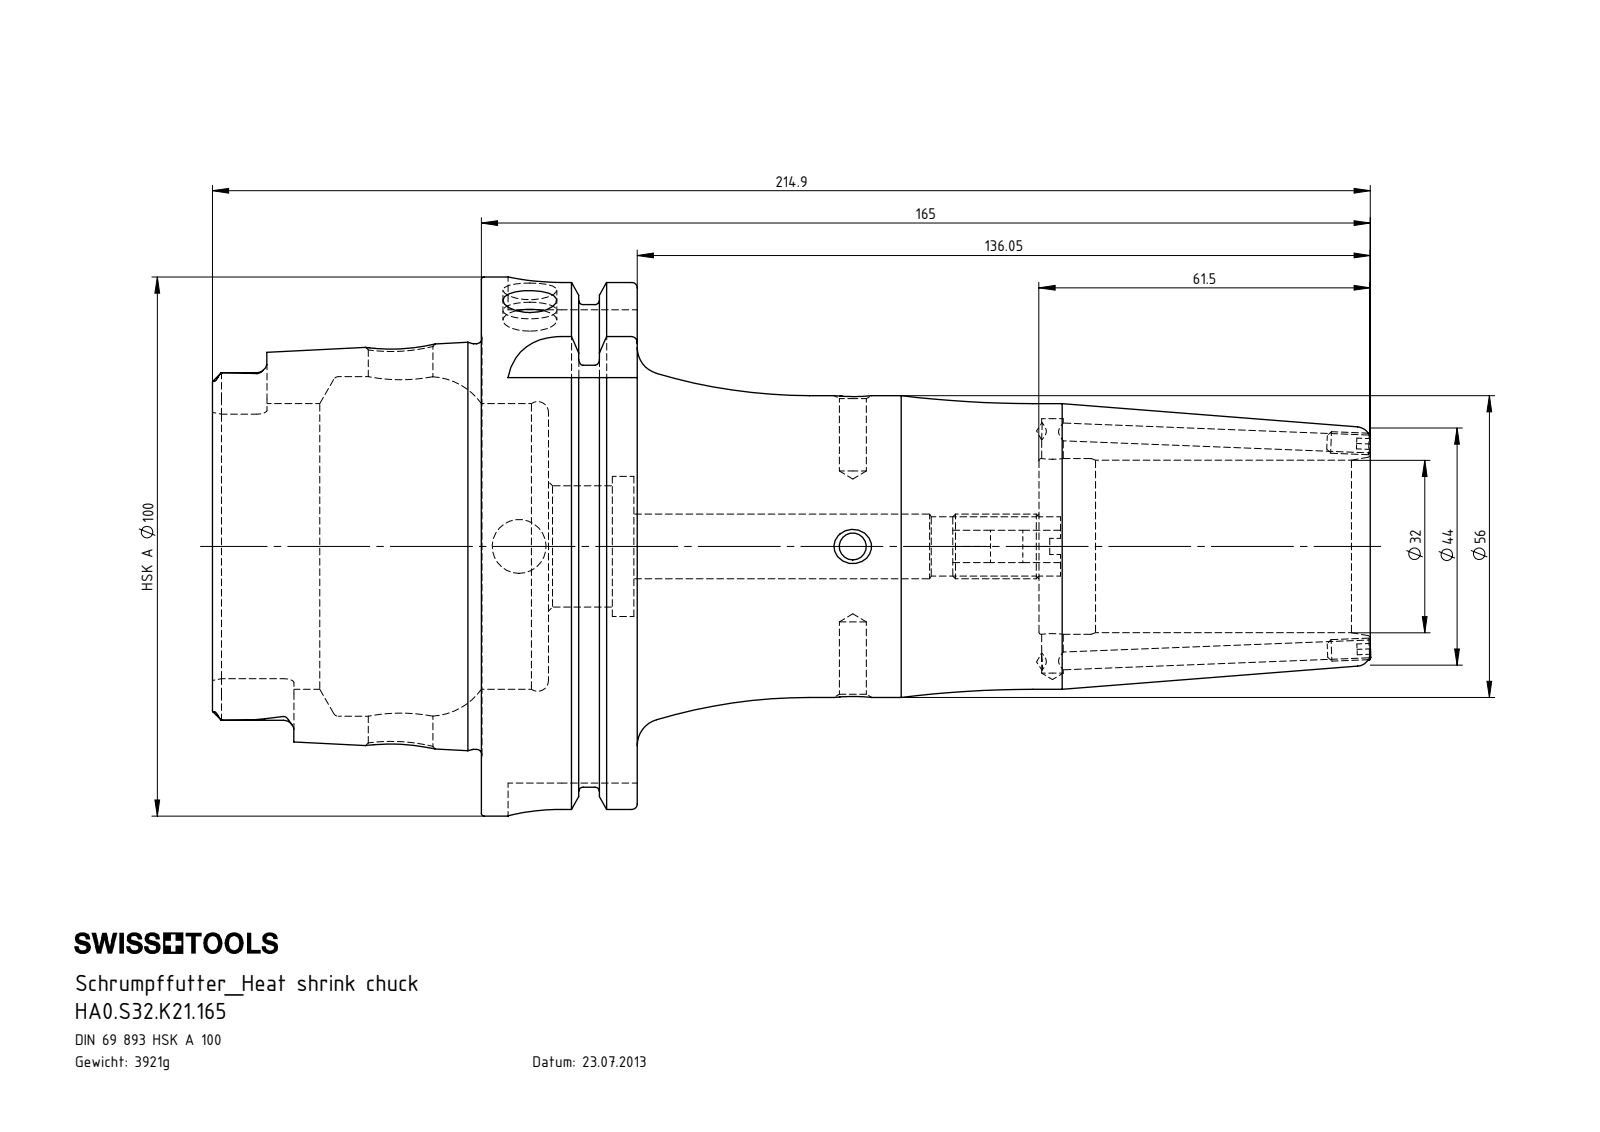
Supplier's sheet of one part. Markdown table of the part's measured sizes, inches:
| quantity | value |
| --- | --- |
| part name | HA0-S32.K21.165_A_Fertigbearbeitung; ERU-AN5.K01.020_A; ERU-CJ3.001.008; HA0.S32.K21.165 |
| STEP written by | SolidWorks 2017 (CONFIG_CONTROL_DESIGN) |
| units | inches |
| bodies | 4 solids, 303 faces (95 planar, 86 cylindrical, 122 other) |
| overall size | 8.465 × 3.937 × 3.937 |
| volume | 30.48 in³ |
| surface area | 128.6 in² |
| round holes (diameter × count) | 0.394 × 3, 0.13 × 2, 0.197 × 2, 0.472 × 2, 0.157 × 1, 0.236 × 1, 0.433 × 1, 0.886 × 1, 1.024 × 1, 1.26 × 1, 1.283 × 1, 2.087 × 1 |
| round bosses / shafts (diameter × count) | 0.157 × 2, 3.937 × 1, 3.62 × 1, 2.963 × 1, 2.205 × 1 |
| partial cylindrical surfaces (radius × count) | 0.075 × 6, 0.192 × 4, 0.394 × 4 |
| main face-to-face distances | 1.14, 0.49, 0.65, 1.965, 2.455, 3.104, 6.039, 4.075, 3.585, 2.935 |
| hole center spacings | 1.459, 2.439, 3.305, 4.764 |
